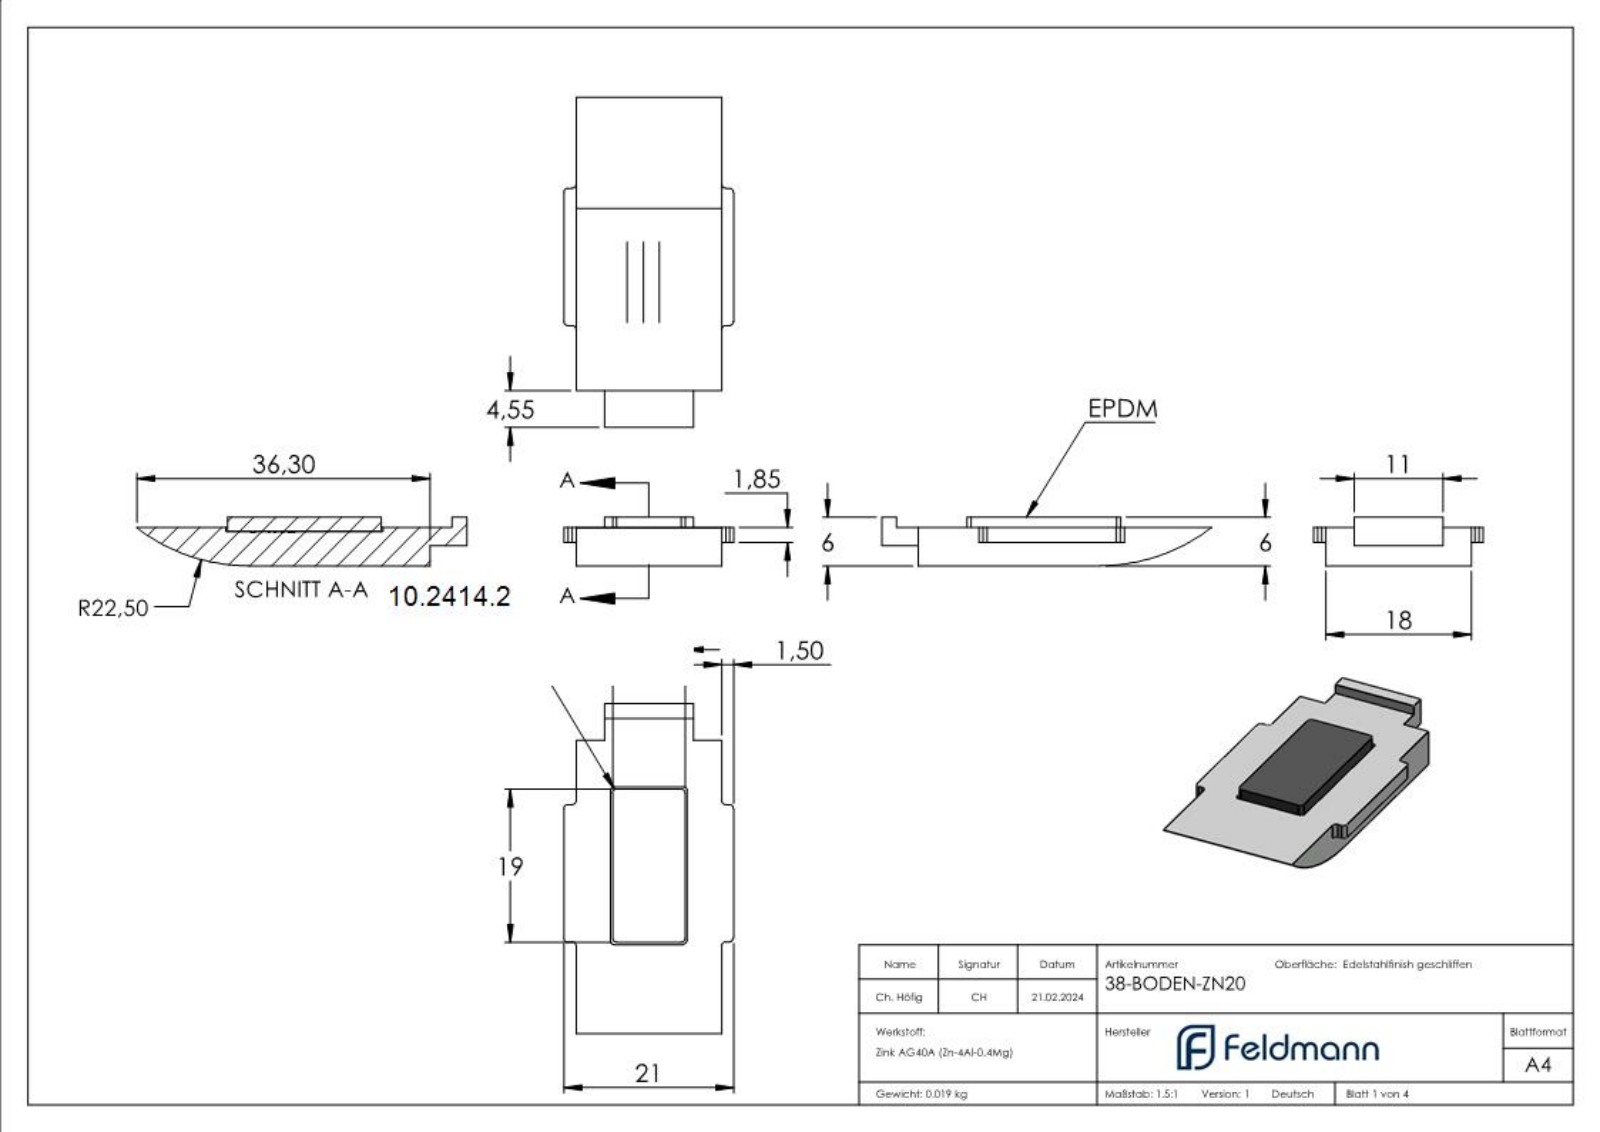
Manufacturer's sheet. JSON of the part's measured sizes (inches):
{"part_name": "38-Boden-ZN20; 38-Boden Gummi auf Boden; 38-Boden ZN20 ohne Gummi", "step_written_by": "SolidWorks 2015 (CONFIG_CONTROL_DESIGN)", "units": "inches", "bodies": {"solids": 2, "faces": 93, "planar": 37, "cylindrical": 34, "other": 22}, "overall_size": [1.587, 0.807, 0.246], "volume_in3": 0.19, "surface_area_in2": 3.759, "partial_cylinders_radius": [[0.02, 28], [0.886, 1]], "face_to_face_distances": [0.187, 0.226, 0.039, 0.689, 0.118, 0.069, 0.108, 0.157, 0.059, 0.144]}
